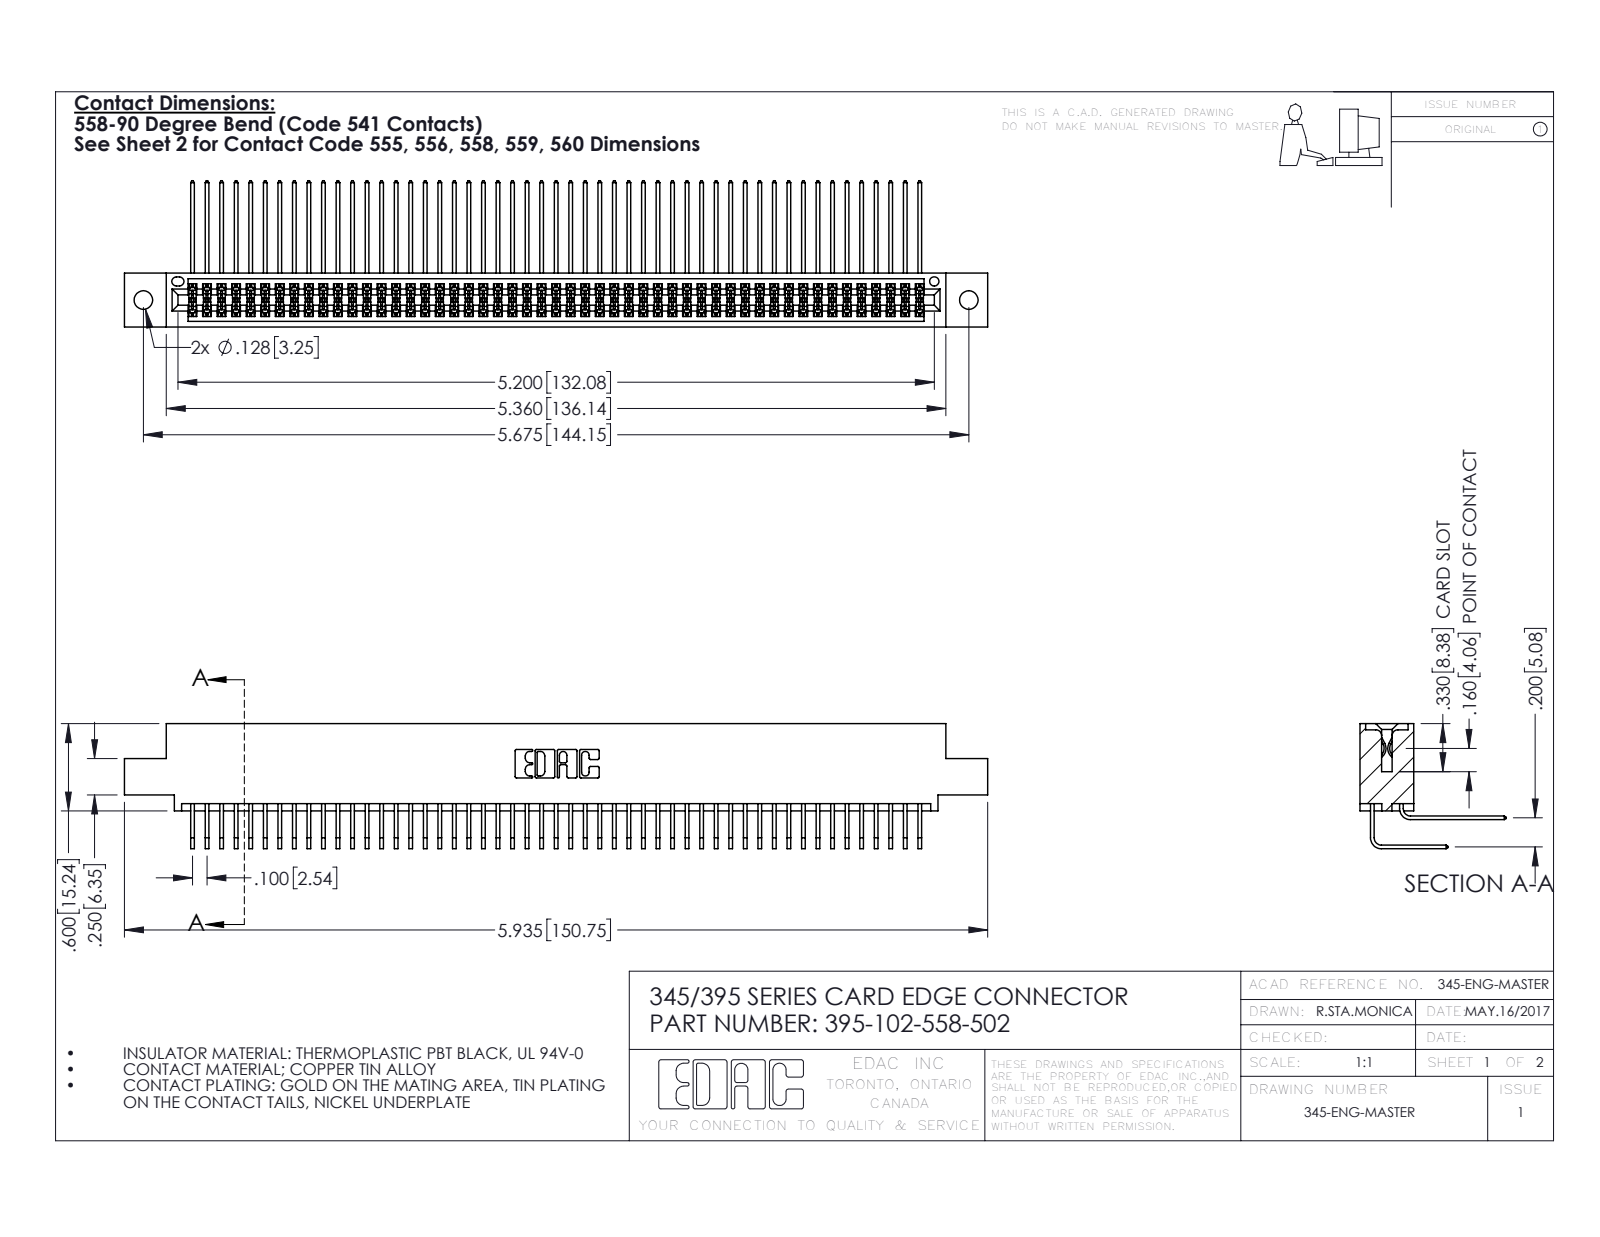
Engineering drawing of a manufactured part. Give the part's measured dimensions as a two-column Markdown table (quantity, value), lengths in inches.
| quantity | value |
| --- | --- |
| part name | 345-292-001_558 Tail - 2; 395-102-558-502; 345-292-001_558 559 Tail - 1; 345 Part_0.110 Offset - 0.128 Dia |
| STEP written by | SolidWorks 2016 (CONFIG_CONTROL_DESIGN) |
| units | inches |
| bodies | 103 solids, 5434 faces (3654 planar, 1780 cylindrical, 0 other) |
| overall size | 5.935 × 1.005 × 0.859 |
| volume | 0.928 in³ |
| surface area | 39.12 in² |
| round holes (diameter × count) | 0.128 × 2, 0.064 × 1 |
| partial cylindrical surfaces (radius × count) | 0.006 × 154, 0.01 × 22, 0.007 × 6, 0.031 × 6, 0.026 × 3, 0.014 × 2, 0.019 × 2, 0.022 × 2 |
| main face-to-face distances | 0.072, 0.298, 0.2, 0.37, 0.098, 0.272, 0.025, 0.225, 0.025, 0.175 |
| hole center spacings | 0.27, 5.439, 5.675 |
